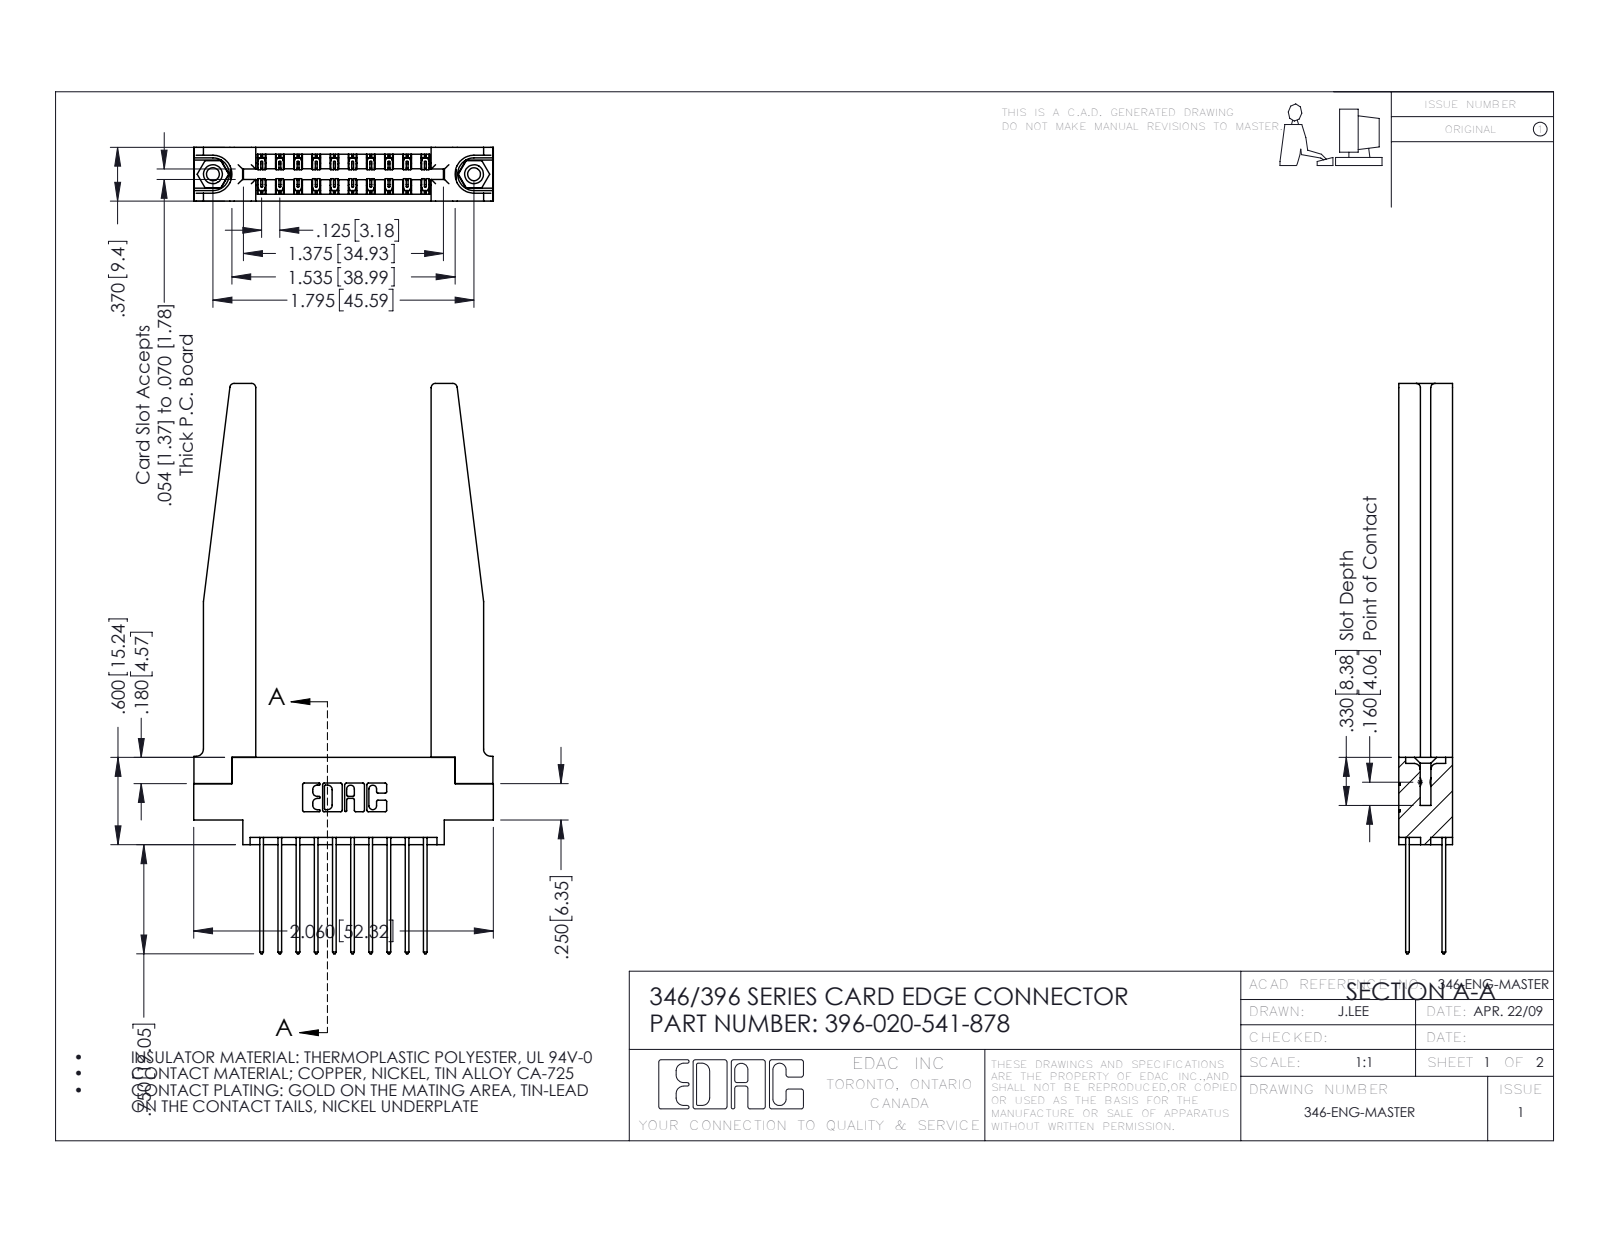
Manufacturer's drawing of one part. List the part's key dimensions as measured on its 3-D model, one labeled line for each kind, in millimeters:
Part name (STEP PRODUCT): 345-292-001_345-293-141; 346-220-078_345-220-078; 346 Part_0.170 Offset - 0.156 Dia-TH; 345-250-001_345-250-001-102 (+1 more)
STEP written by: SolidWorks 2016 (CONFIG_CONTROL_DESIGN)
Units: millimetres
Bodies: 25 solids, 1400 faces (922 planar, 426 cylindrical, 52 other)
Overall size (bounding box): 99.6 × 52.3 × 9.4
Volume: 11 700 mm³ · Surface area: 13 380 mm²
Round holes (diameter × count): ⌀2.3 ×2, ⌀3.2 ×2, ⌀4 ×2, ⌀1.6 ×1
Round bosses / shafts (diameter × count): ⌀3.9 ×2
Partial cylindrical surfaces — rounded edges, fillets, slot ends (radius × count): R0.2 ×30, R0.3 ×22, R0.3 ×20, R0.8 ×8, R0.2 ×6, R0.8 ×6, R0.7 ×3, R0.4 ×2
Main face-to-face distances: 9.4, 3.8, 3.8, 1.8, 1.2, 8.2, 6.4, 2.6, 5.6, 4.4
Hole centre spacings: 6.2, 40.4, 45.6
